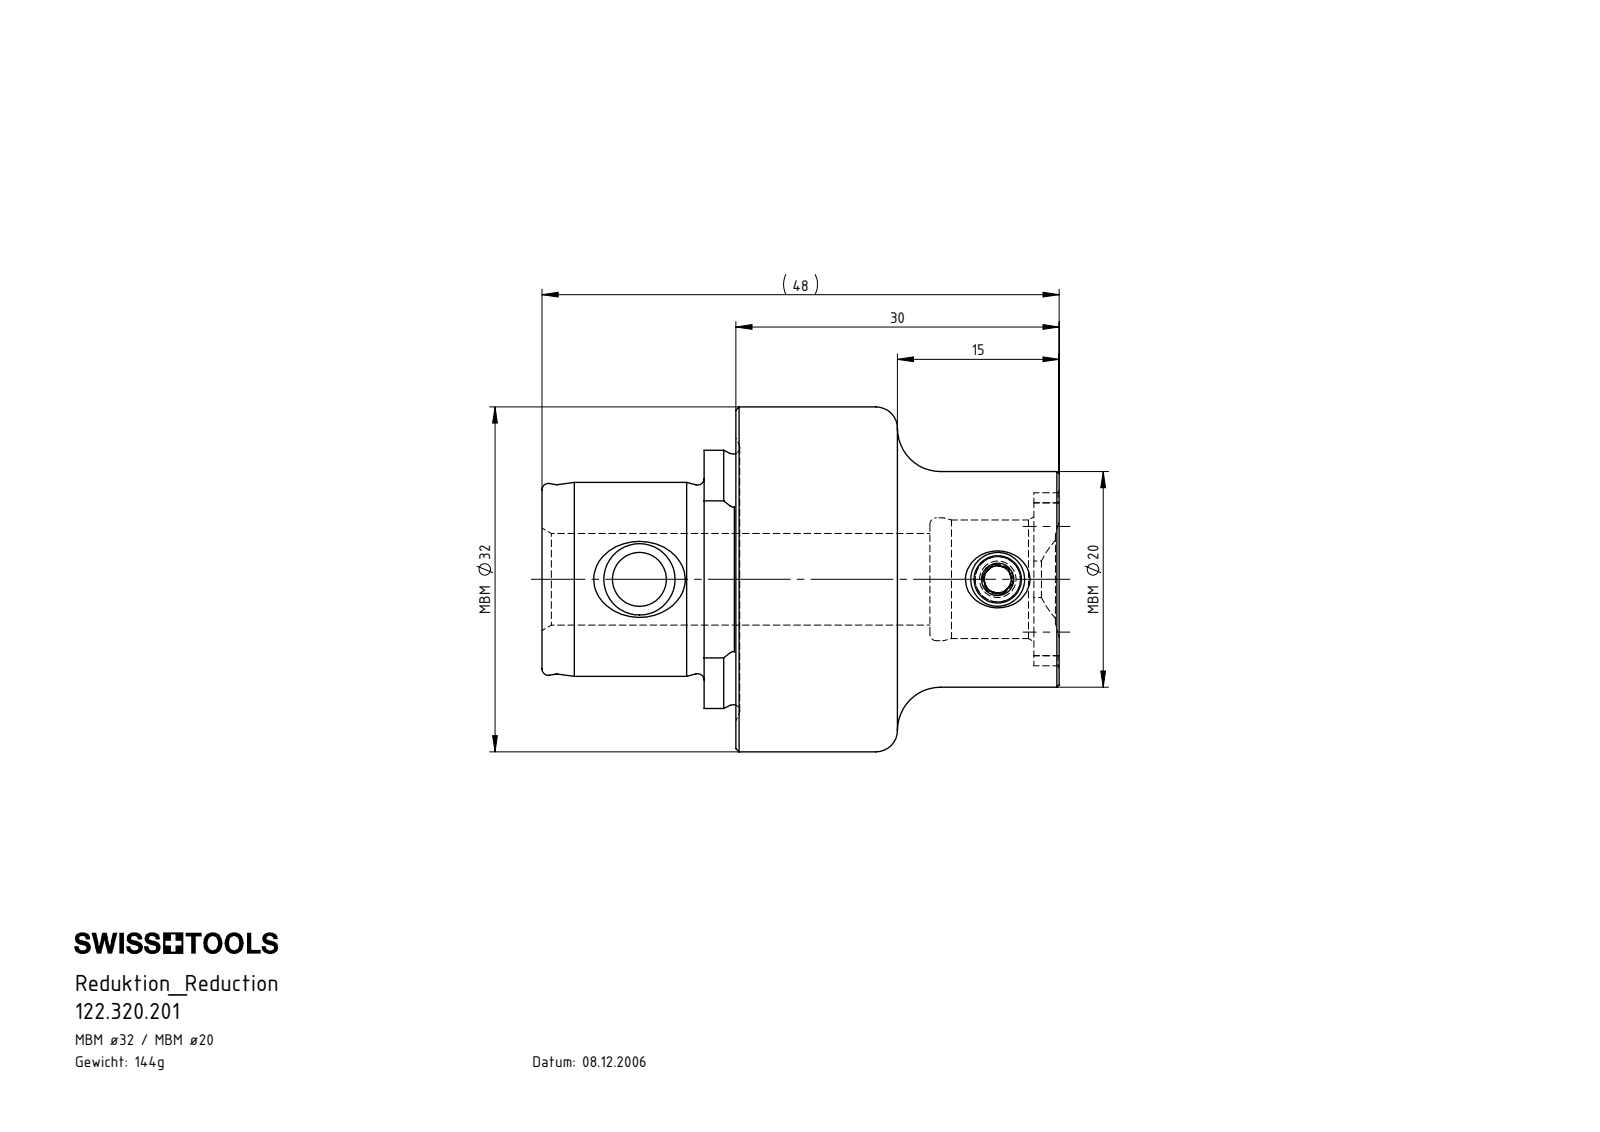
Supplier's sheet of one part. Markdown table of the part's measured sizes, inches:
| quantity | value |
| --- | --- |
| part name | MB3-MB1.K01.030; MB1-ER1.001.006_A; MB3-MB1.K01.030_A |
| STEP written by | SolidWorks 2012 (CONFIG_CONTROL_DESIGN) |
| units | inches |
| bodies | 2 solids, 126 faces (24 planar, 32 cylindrical, 70 other) |
| overall size | 1.89 × 1.26 × 1.26 |
| volume | 1.119 in³ |
| surface area | 9.905 in² |
| round holes (diameter × count) | 0.165 × 1, 0.197 × 1, 0.335 × 1, 0.433 × 1, 0.449 × 1 |
| round bosses / shafts (diameter × count) | 1.26 × 1, 0.787 × 1, 0.709 × 1, 0.197 × 1 |
| partial cylindrical surfaces (radius × count) | 0.087 × 4, 0.256 × 1, 0.316 × 1, 0.471 × 1 |
| main face-to-face distances | 0.709, 0.593, 0.116, 1.89, 1.297, 1.181, 1.797, 1.205, 1.089, 0.093 |
| hole center spacings | 1.309 |
